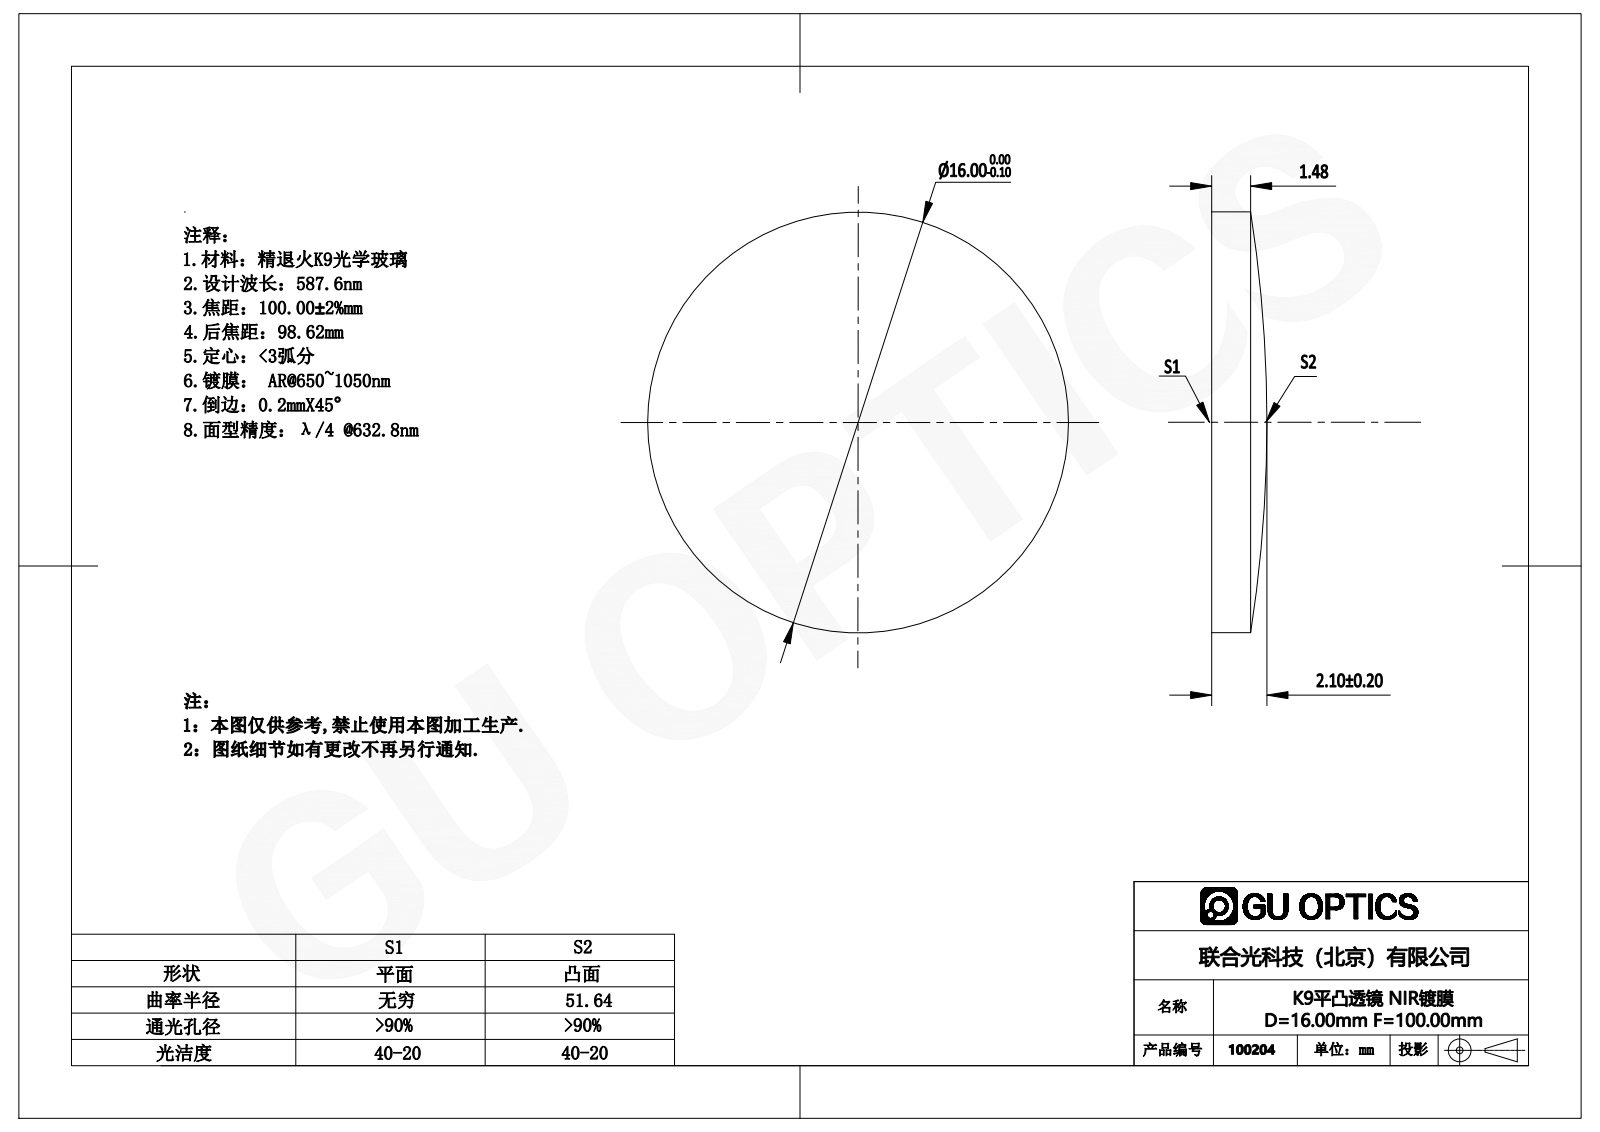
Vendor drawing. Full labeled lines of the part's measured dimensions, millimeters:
Part name (STEP PRODUCT): 100204
STEP written by: SolidWorks 2016 (AUTOMOTIVE_DESIGN)
Units: millimetres
Bodies: 1 solid, 5 faces (1 planar, 2 cylindrical, 2 other)
Overall size (bounding box): 16 × 16 × 2.1
Volume: 360 mm³ · Surface area: 478 mm²
Round bosses / shafts (diameter × count): ⌀16 ×1
